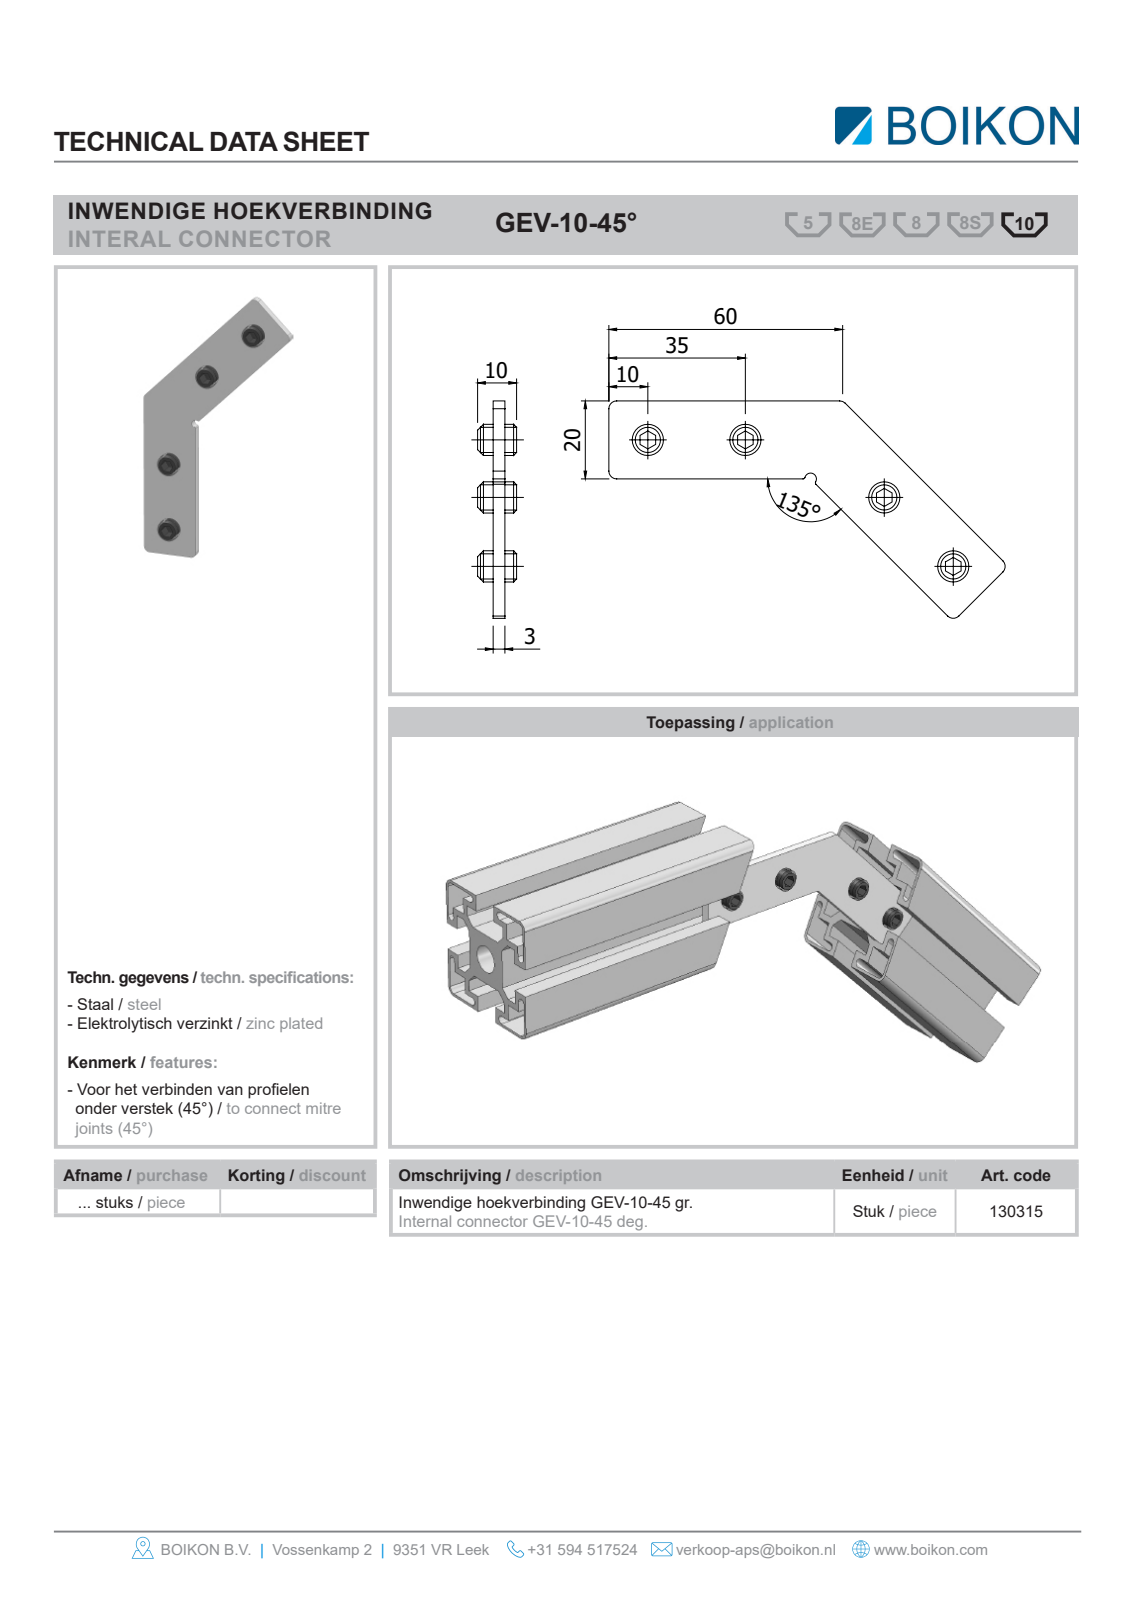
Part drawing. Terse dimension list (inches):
name: Root; 130315Inwendige hoekverbinding GEV-10 45grBOIKON; 901112Binnenzesk. DIN 916 EV M8 x 10BOIKON0
written by: HiCAD 2013 1802.4 Build 509 (AUTOMOTIVE_DESIGN)
unit: in
bodies: 5 solids, 56 faces (40 planar, 8 cylindrical, 8 other)
size: 4.033 × 2.227 × 0.768
volume: 0.432 in³; area: 10.05 in²
holes: 4× ⌀0.315
bosses: 4× ⌀0.255
face distances: 0.118, 0.787, 0.157, 0.236, 0.197, 0.079, 0.039, 0.492, 0.984, 2.386
hole spacings: 0.984, 2.456, 1.517, 3.336
